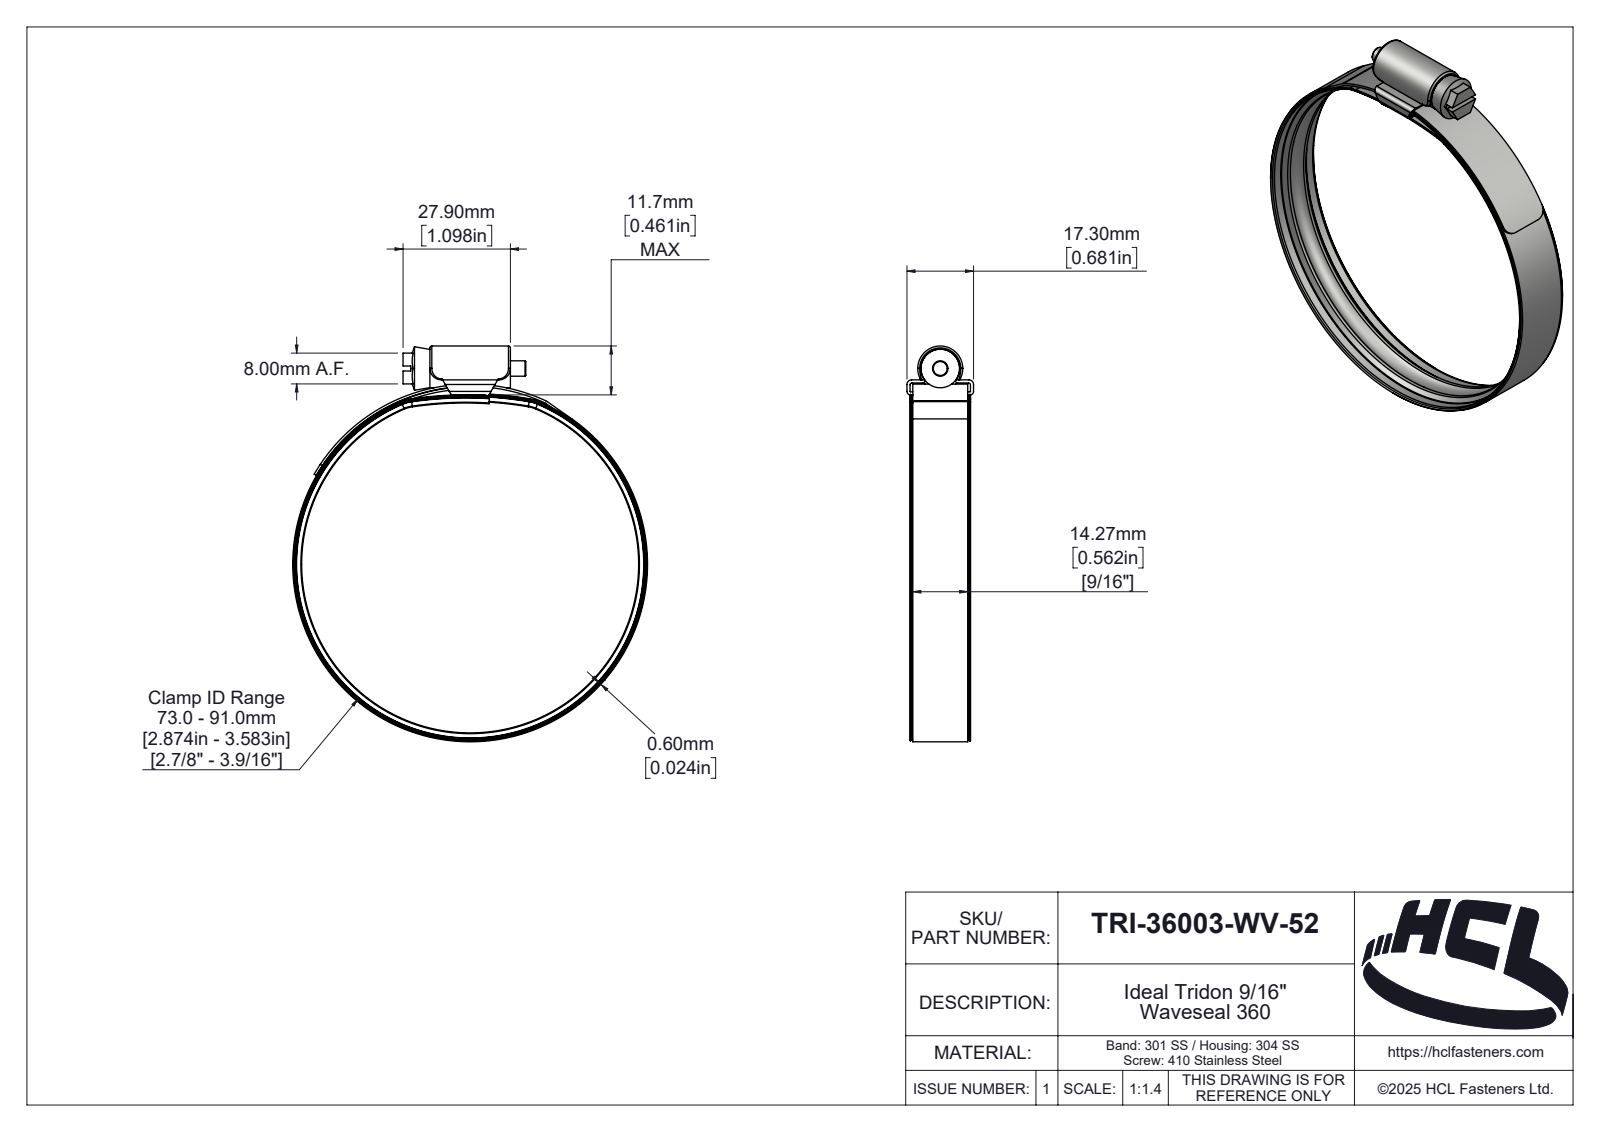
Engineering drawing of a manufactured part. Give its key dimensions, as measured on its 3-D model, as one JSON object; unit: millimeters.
{"part_name": "TRI-36003-WV-52", "step_written_by": "SolidWorks 2025 (AUTOMOTIVE_DESIGN)", "units": "millimeters", "bodies": {"solids": 4, "faces": 418, "planar": 42, "cylindrical": 119, "other": 257}, "overall_size": [102.8, 92.2, 17.3], "volume_mm3": 6760, "surface_area_mm2": 23229, "round_holes": [[90.4, 1], [91, 1]], "round_bosses_or_shafts": [[92.2, 1], [90.8, 1], [10, 1], [4, 1]], "partial_cylinders_radius": [[0.5, 6], [3, 4], [0.1, 2], [0.9, 2], [1.2, 2], [9.9, 2], [10.1, 2], [0.46, 1]], "face_to_face_distances": [0.8, 14.26, 3.1, 0.6, 2.3, 3.9, 27.9, 1.52, 15.78, 16.5]}
